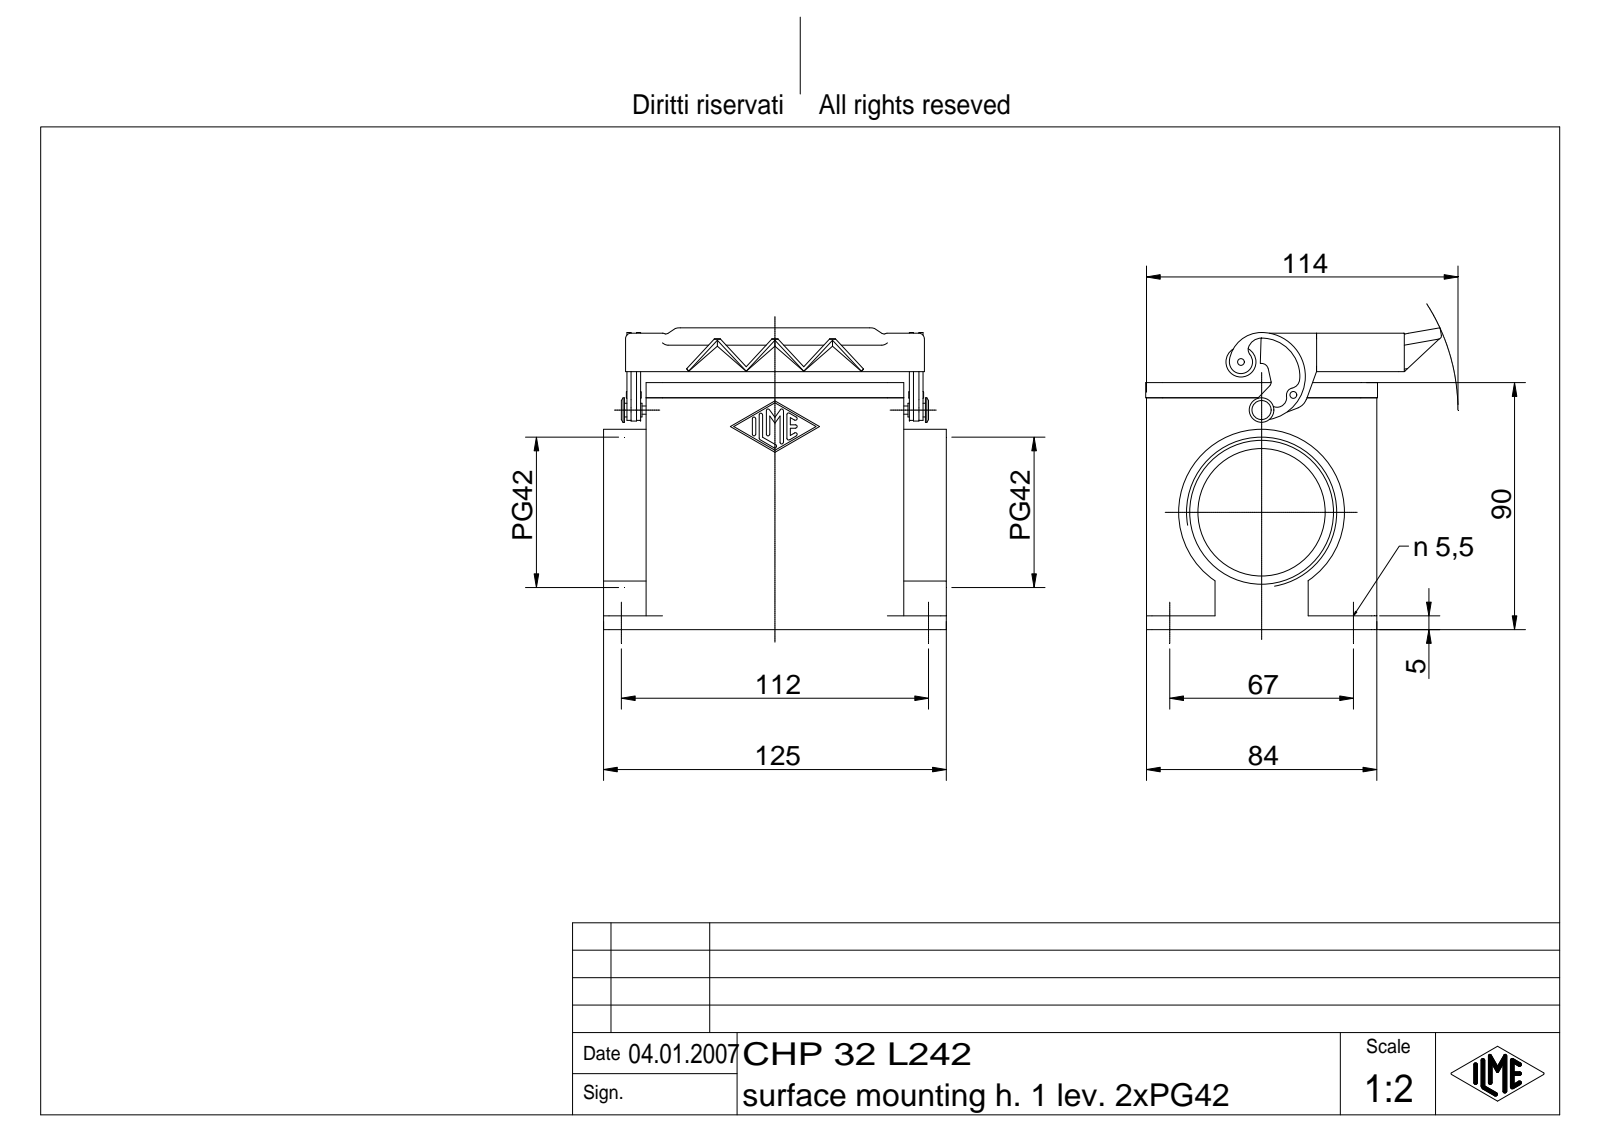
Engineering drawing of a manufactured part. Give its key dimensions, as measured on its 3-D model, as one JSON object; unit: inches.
{"part_name": "CHP 32 L242", "step_written_by": "Autodesk Inventor 7 (AUTOMOTIVE_DESIGN)", "units": "inches", "bodies": {"solids": 4, "faces": 491, "planar": 166, "cylindrical": 145, "other": 180}, "overall_size": [4.921, 4.33, 4.246], "volume_in3": 14.45, "surface_area_in2": 165.4, "round_holes": [[0.217, 4], [0.079, 1], [1.83, 1], [2.066, 1]], "round_bosses_or_shafts": [[2.382, 1], [0.433, 1], [0.354, 1], [0.197, 1], [0.118, 1], [0.098, 1]], "partial_cylinders_radius": [[0.079, 16], [0.024, 14], [0.059, 9], [0.236, 8], [0.006, 4], [0.118, 4], [0.039, 3], [0.098, 3]], "face_to_face_distances": [0.118, 3.189, 3.307, 0.157, 3.071, 0.453, 3.248, 3.327, 2.795, 3.169], "hole_center_spacings": [2.638, 4.409, 5.138, 1.744]}
